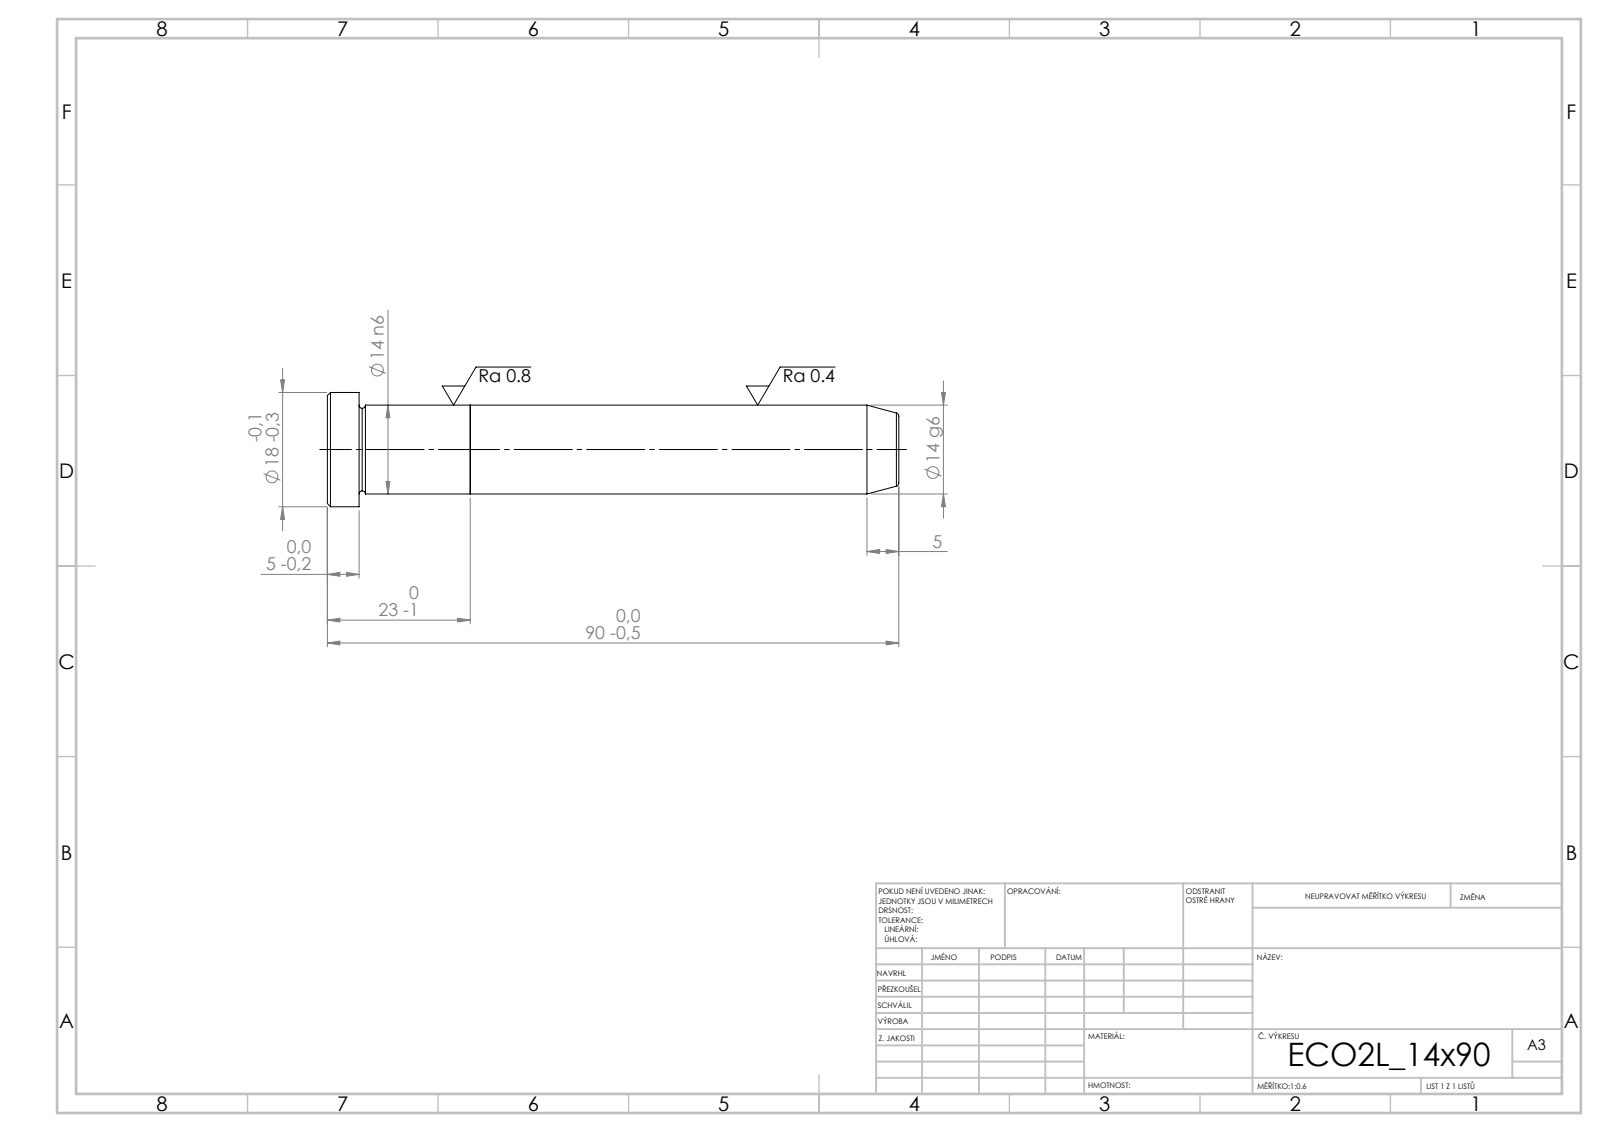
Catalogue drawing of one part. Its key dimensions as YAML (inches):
step_written_by: "SolidWorks 2019 (CONFIG_CONTROL_DESIGN)"
units: inches
bodies: {solids: 2, faces: 21, planar: 5, cylindrical: 6, other: 10}
overall_size: [3.543, 0.709, 0.709]
volume: 0.866
surface_area: 7.397
round_bosses_or_shafts:
  - {diameter: 0.709, count: 1}
  - {diameter: 0.551, count: 1}
face_to_face_distances: [0.886, 0.689, 0.197, 2.657, 3.346, 3.543]
